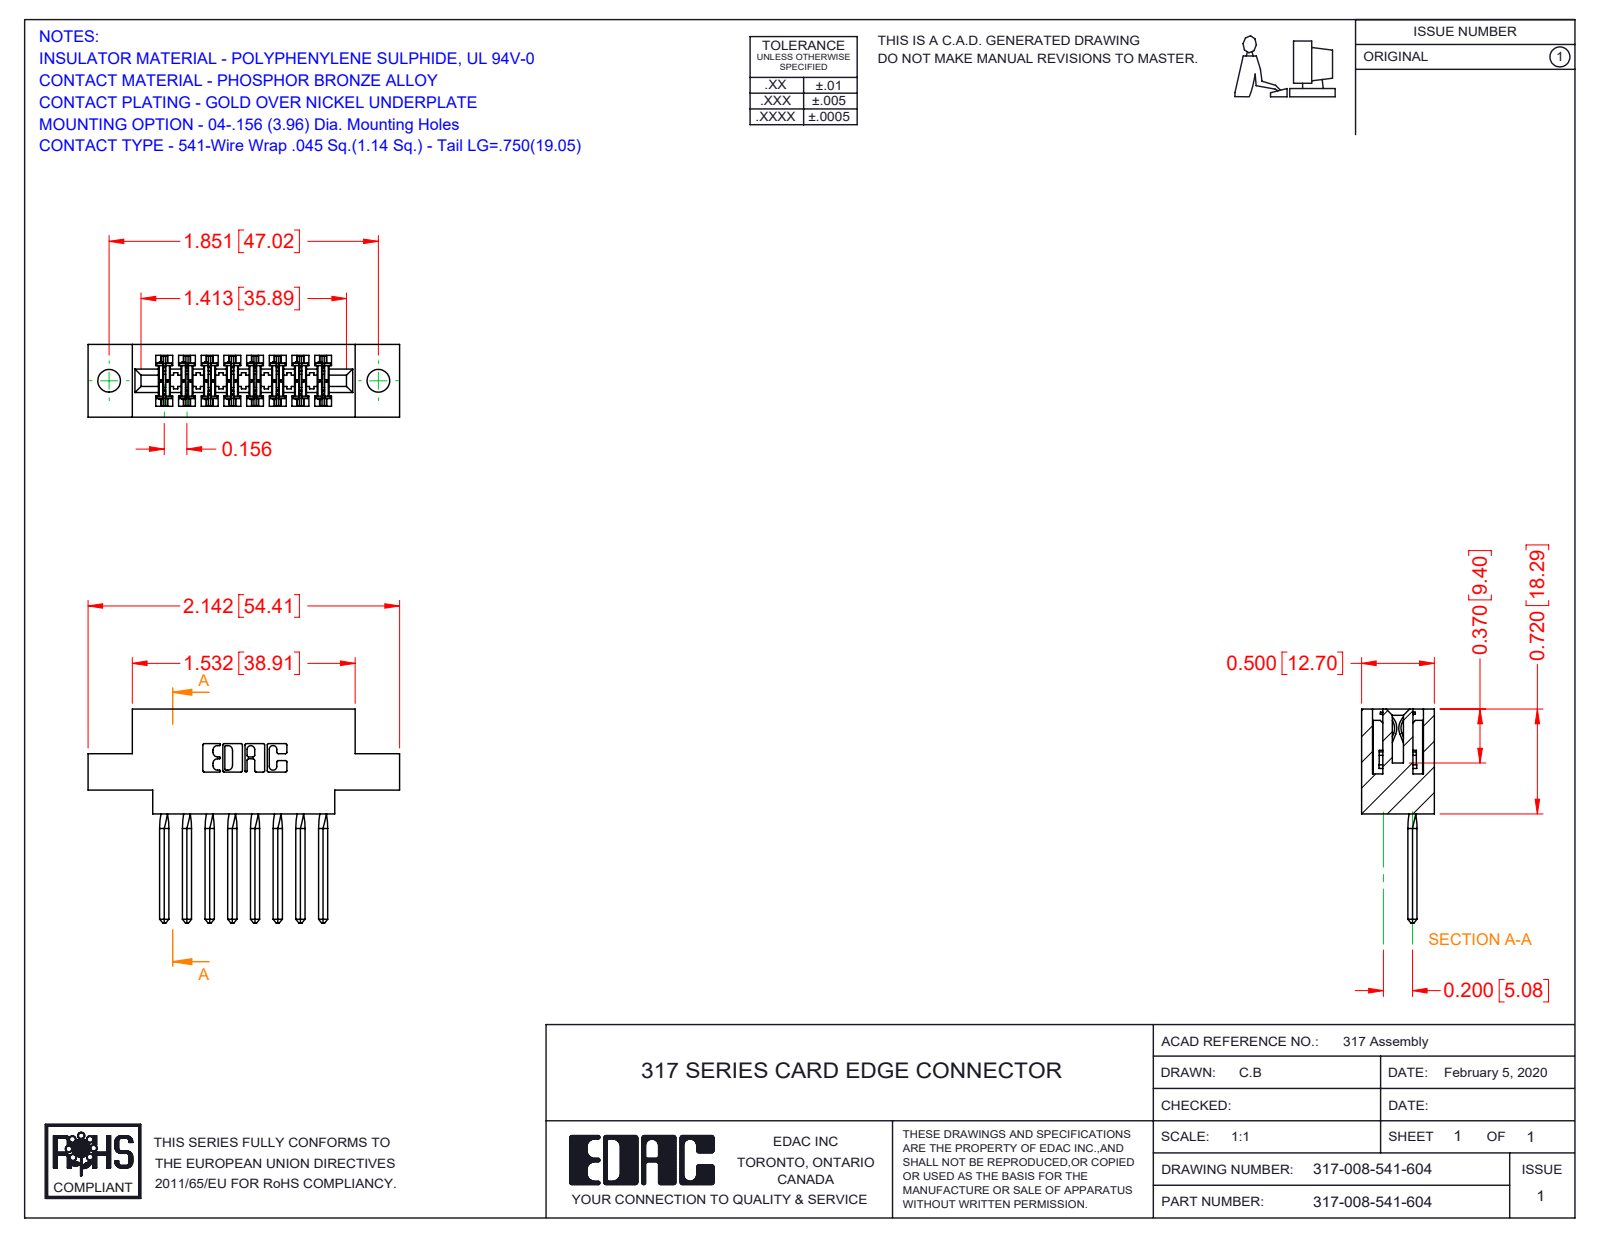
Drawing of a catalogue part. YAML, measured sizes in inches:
part_name: "317-290-002_541; 317 Part_.156 Dia - TH; 317-008-541-604"
step_written_by: "SolidWorks 2016 (CONFIG_CONTROL_DESIGN)"
units: inches
bodies: {solids: 9, faces: 1318, planar: 1050, cylindrical: 236, other: 32}
overall_size: [2.142, 1.47, 0.5]
volume: 0.469
surface_area: 14.8
round_holes:
  - {diameter: 0.156, count: 2}
partial_cylinders:
  - {radius: 0.01, count: 22}
  - {radius: 0.015, count: 16}
  - {radius: 0.007, count: 6}
  - {radius: 0.031, count: 6}
  - {radius: 0.026, count: 3}
  - {radius: 0.095, count: 2}
  - {radius: 0.1, count: 2}
  - {radius: 0.11, count: 2}
face_to_face_distances: [0.5, 0.075, 0.425, 0.11, 0.065, 0.22, 0.156, 0.331, 0.116, 0.35]
hole_center_spacings: [1.851]
